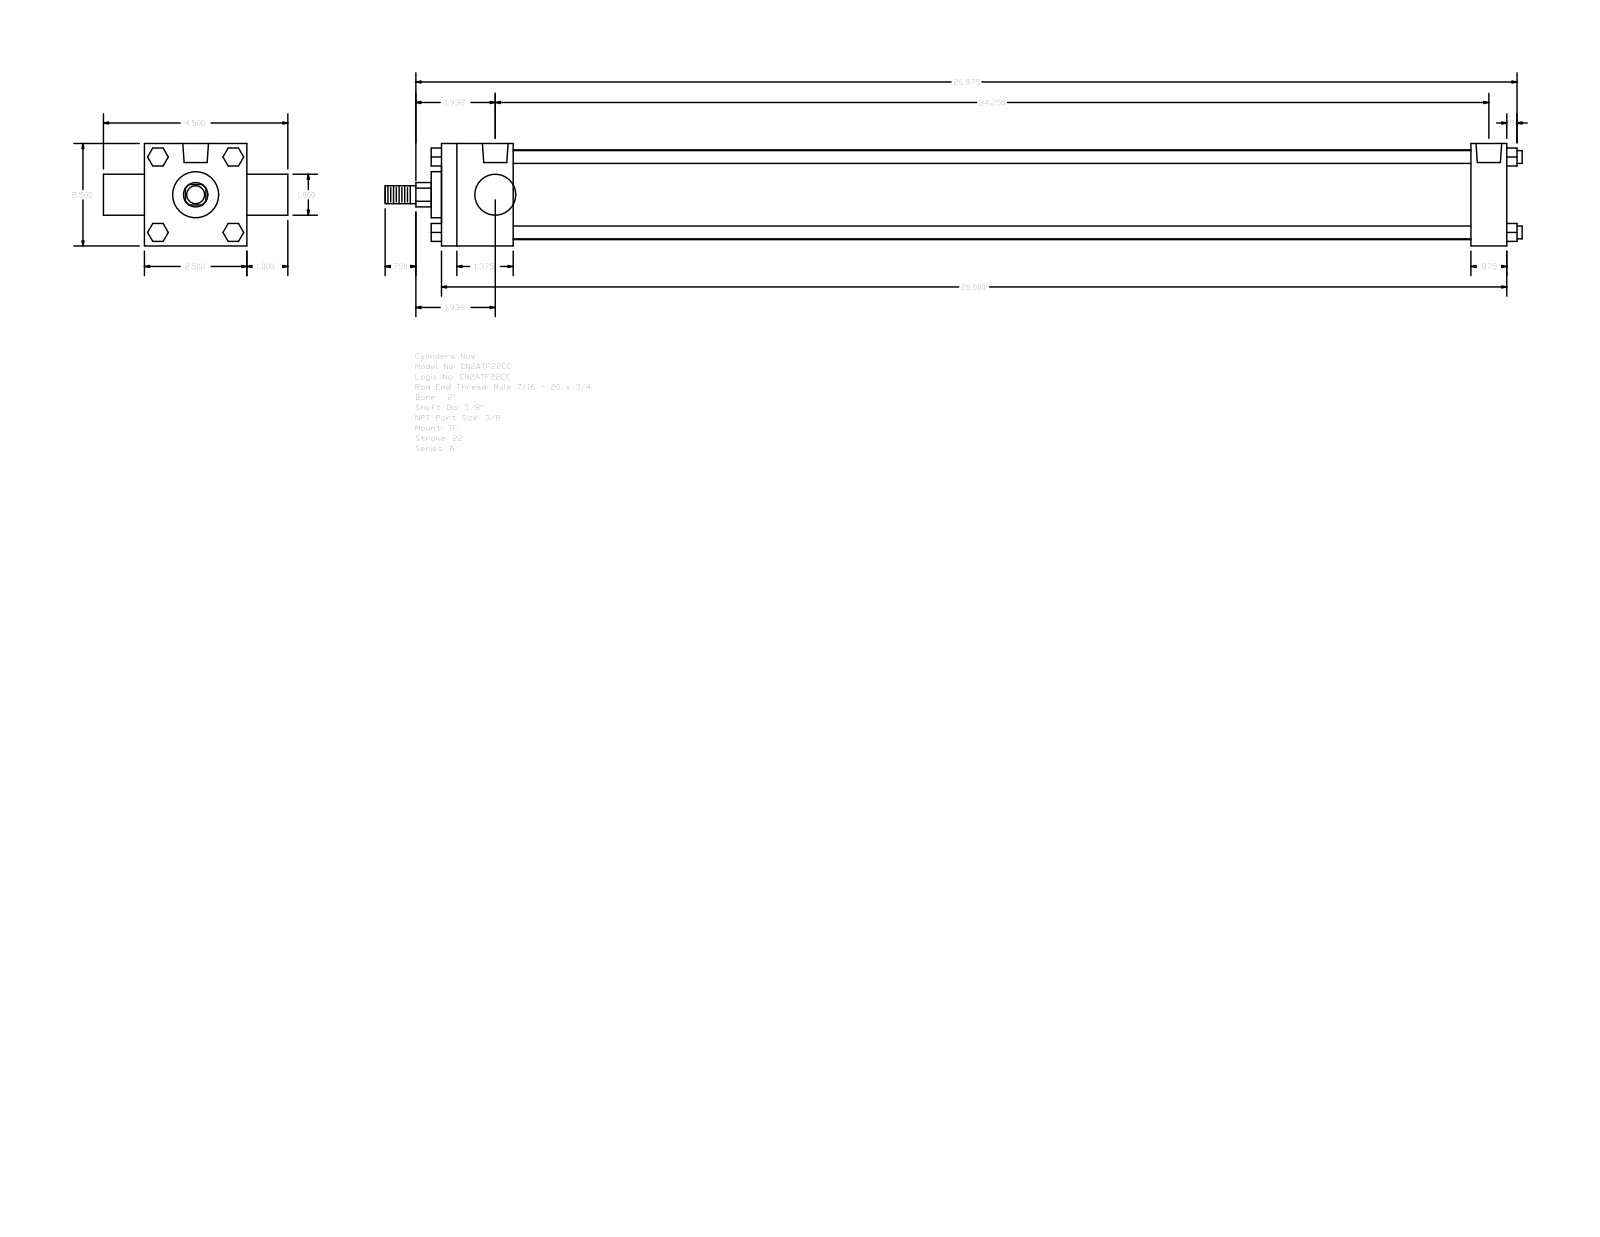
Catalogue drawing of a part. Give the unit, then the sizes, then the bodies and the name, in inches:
Units: inches
Overall size (bounding box): 27.75 × 4.5 × 2.5
Round holes (diameter × count): ⌀0.219 ×3, ⌀0.627 ×2
Round bosses / shafts (diameter × count): ⌀0.313 ×4, ⌀2.19 ×1, ⌀1.125 ×1, ⌀1 ×1, ⌀0.625 ×1, ⌀0.437 ×1
Partial cylindrical surfaces — rounded edges, fillets, slot ends (radius × count): R0.297 ×1
Main face-to-face distances: 2.5, 26, 1.75, 25.125, 23.375, 24.25, 0.875, 1, 3.5, 0.25
Hole centre spacings: 0.156, 0.157, 23.937, 24.093, 24.094, 24.25
Bodies: 0 solids, 120 faces (92 planar, 28 cylindrical, 0 other)
Part name (STEP PRODUCT): A_TF__0200_0.625
STEP written by: GSSL Pune (CONFIG_CONTROL_DESIGN)
